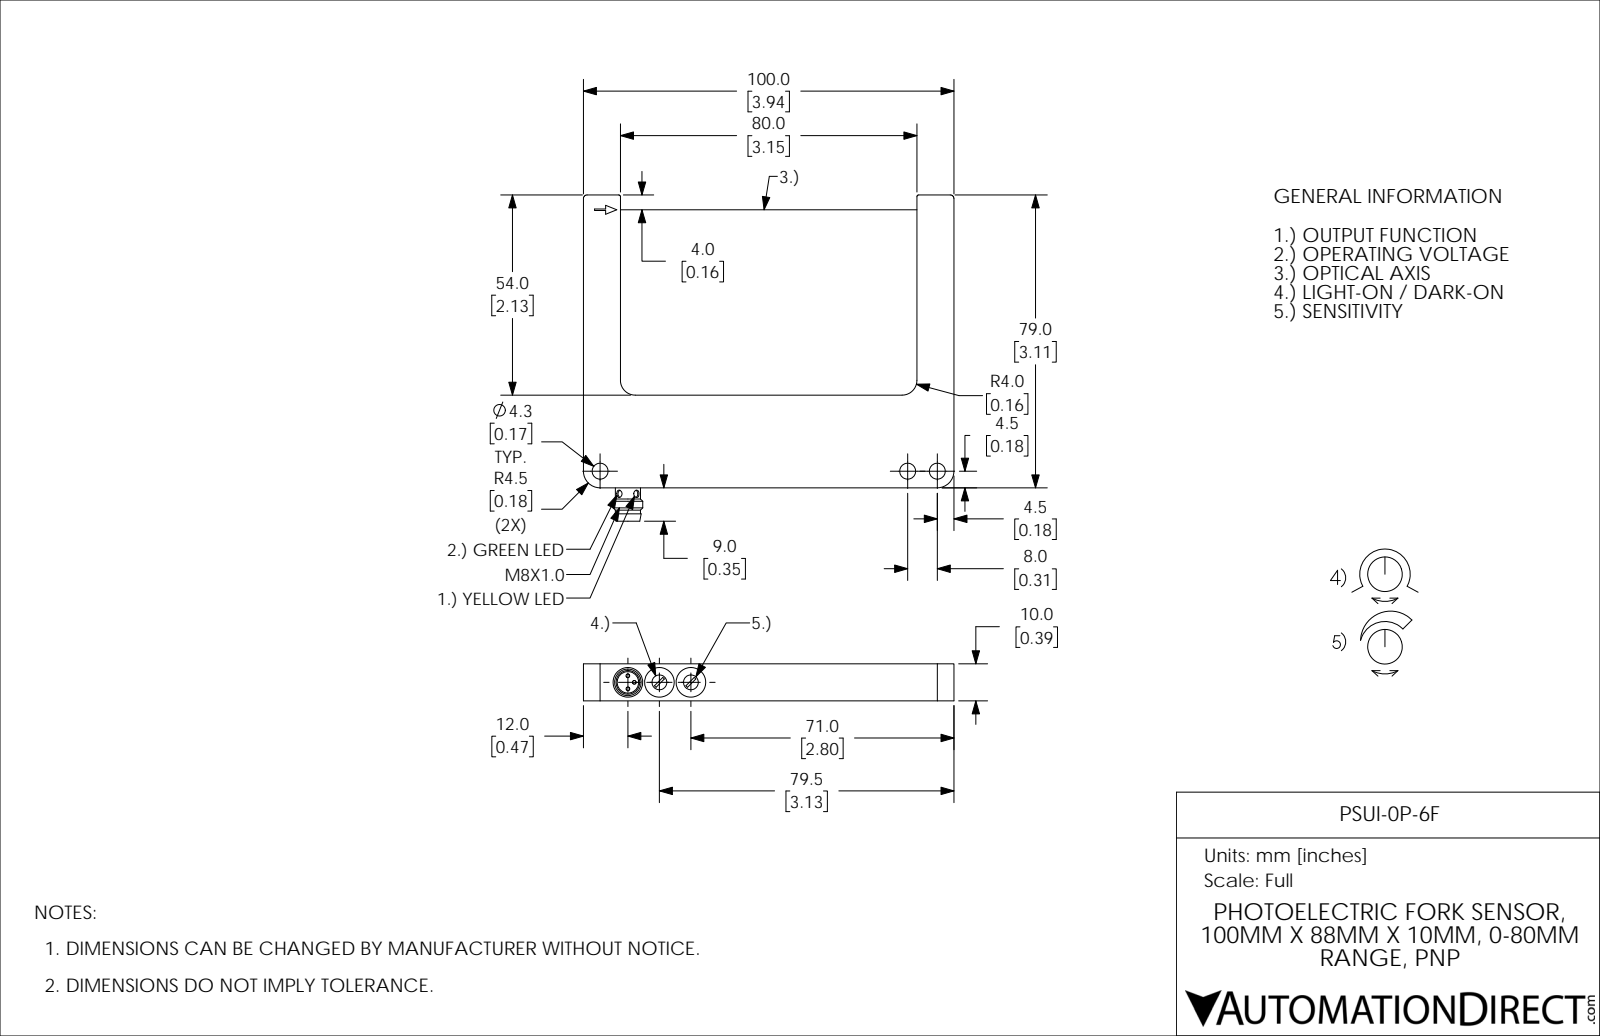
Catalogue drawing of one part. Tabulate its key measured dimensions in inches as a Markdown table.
| quantity | value |
| --- | --- |
| part name | PSUI-0P-6F |
| STEP written by | SolidWorks 2017 (AUTOMOTIVE_DESIGN) |
| units | inches |
| bodies | 1 solid, 71 faces (35 planar, 30 cylindrical, 6 other) |
| overall size | 3.937 × 3.465 × 0.394 |
| volume | 2.17 in³ |
| surface area | 19.25 in² |
| round holes (diameter × count) | 0.169 × 3, 0.079 × 2, 0.157 × 2, 0.315 × 2, 0.228 × 1 |
| round bosses / shafts (diameter × count) | 0.039 × 3, 0.315 × 1, 0.267 × 1 |
| partial cylindrical surfaces (radius × count) | 0.02 × 2, 0.039 × 2, 0.063 × 2, 0.157 × 2, 0.177 × 2 |
| main face-to-face distances | 0.394, 3.543, 3.937, 0.984, 3.15, 2.126, 3.11, 3.106, 0.98, 0.157 |
| hole center spacings | 0.335, 0.315, 0.669, 3.268, 3.583 |
